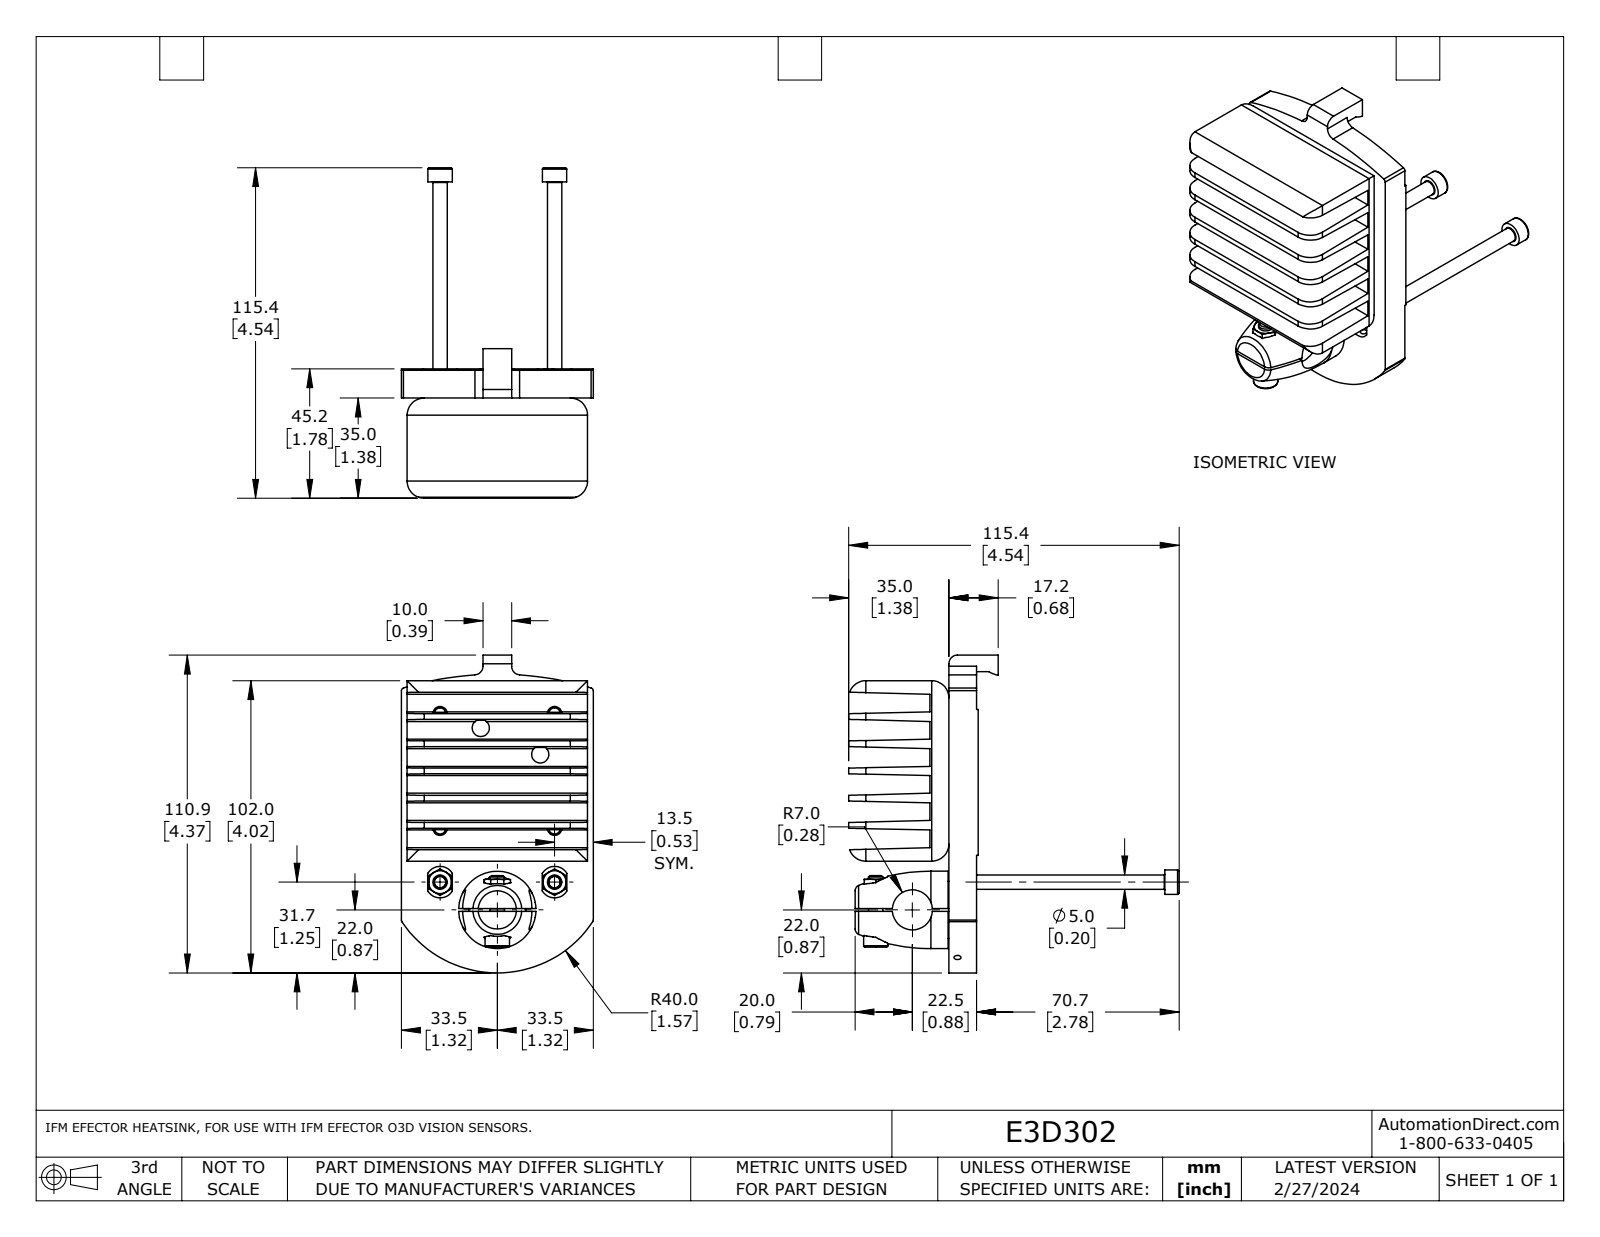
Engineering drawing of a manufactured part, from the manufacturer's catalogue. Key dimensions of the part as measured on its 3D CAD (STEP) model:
Part name (STEP PRODUCT): E3D302
STEP written by: SolidWorks 2023 (AUTOMOTIVE_DESIGN)
Units: inches
Bodies: 10 solids, 387 faces (215 planar, 99 cylindrical, 73 other)
Overall size (bounding box): 4.543 × 4.367 × 2.638
Volume: 8.238 in³ · Surface area: 96.94 in²
Round holes (diameter × count): ⌀0.197 ×6, ⌀0.163 ×3, ⌀0.098 ×2, ⌀0.236 ×2, ⌀0.217 ×1, ⌀0.295 ×1, ⌀0.551 ×1, ⌀0.709 ×1, ⌀0.945 ×1
Round bosses / shafts (diameter × count): ⌀0.38 ×4, ⌀0.335 ×3, ⌀0.197 ×3, ⌀1.063 ×1, ⌀0.787 ×1
Partial cylindrical surfaces — rounded edges, fillets, slot ends (radius × count): R0.236 ×8, R0.118 ×7, R0.039 ×4, R0.197 ×4, R0.344 ×2, R0.169 ×1, R0.433 ×1, R0.472 ×1
Main face-to-face distances: 0.374, 0.748, 0.402, 0.02, 0.382, 0.642, 0.661, 0.26, 2.48, 0.079
Hole centre spacings: 1.575, 0.787, 1.761, 0.593, 0.741, 0.875, 1.034, 1.081
